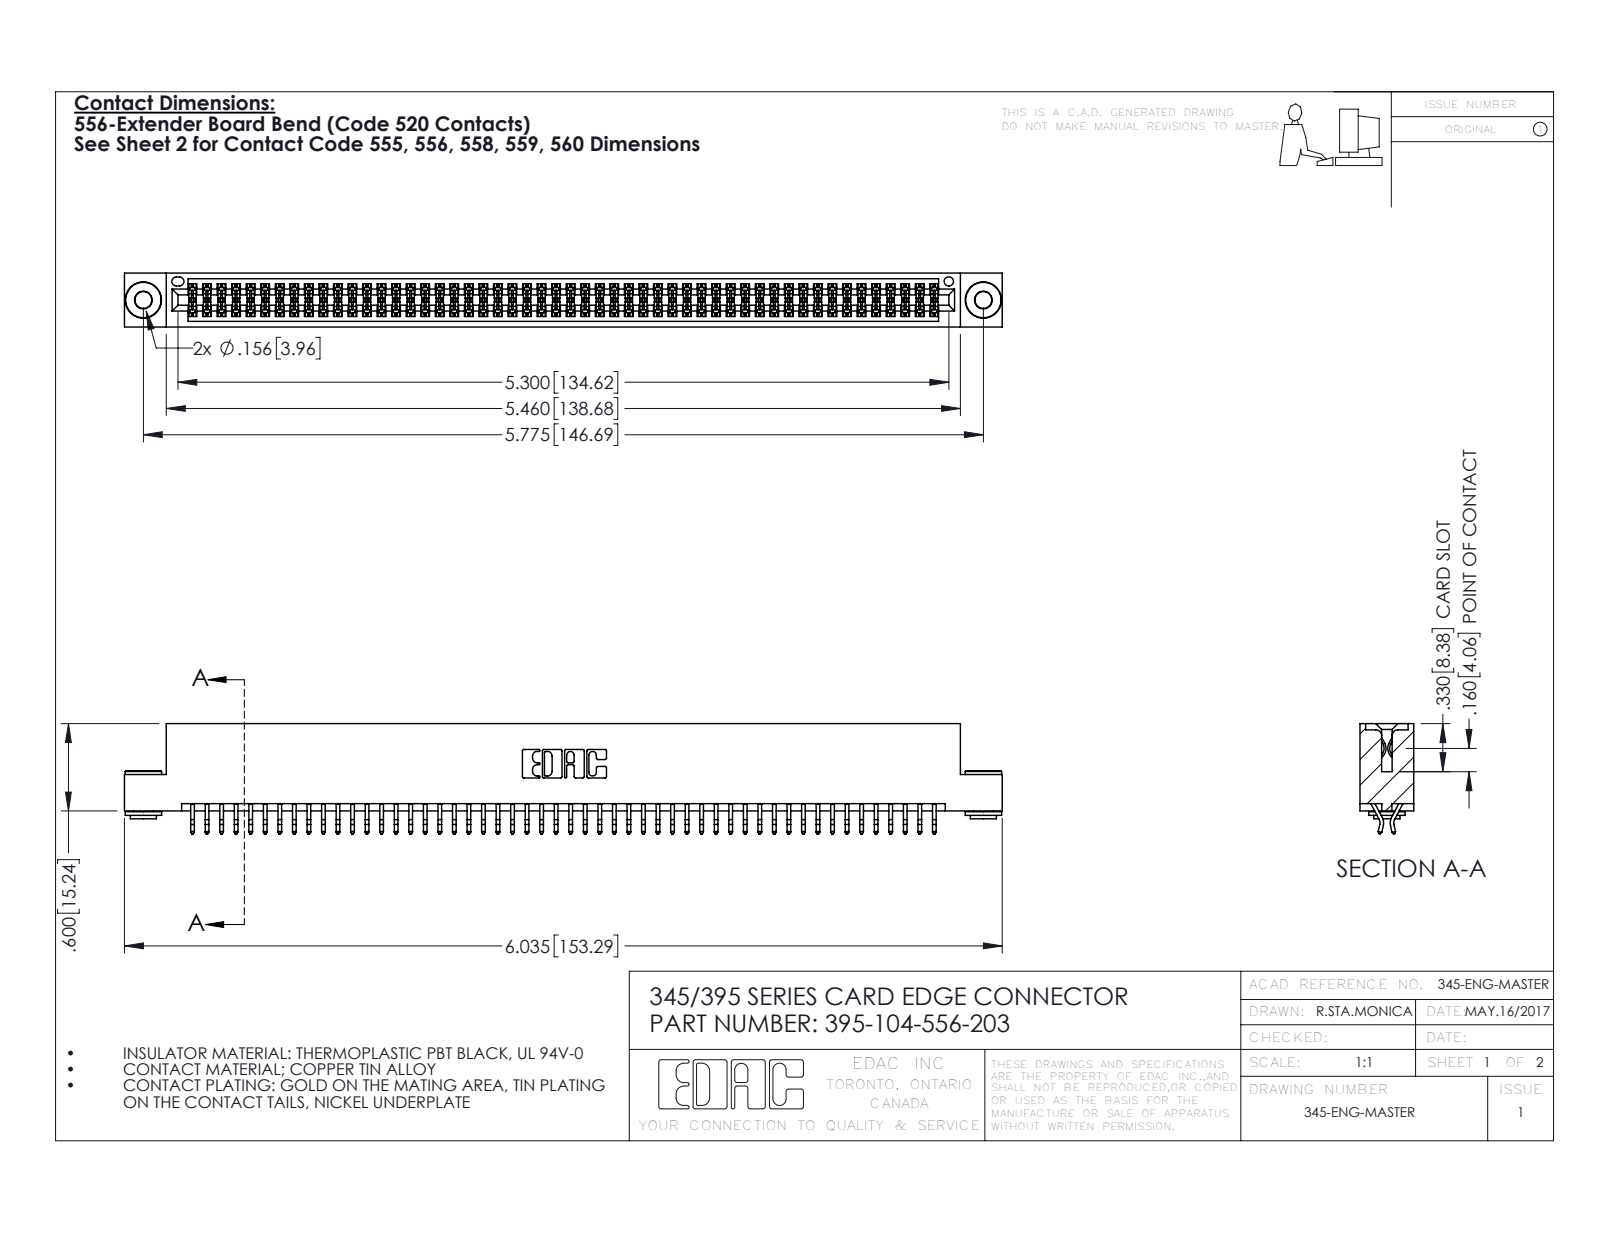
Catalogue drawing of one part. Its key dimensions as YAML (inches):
part_name: "345-250-002_345-250-002-102; 345-292-001_556 Tail; 395-104-556-203; 345 Part_Flush Mounting Lugs - 0.156 Dia-TH"
step_written_by: "SolidWorks 2016 (CONFIG_CONTROL_DESIGN)"
units: inches
bodies: {solids: 107, faces: 5988, planar: 3938, cylindrical: 2042, other: 8}
overall_size: [6.035, 0.757, 0.37]
volume: 0.915
surface_area: 34.84
round_holes:
  - {diameter: 0.116, count: 2}
  - {diameter: 0.156, count: 2}
  - {diameter: 0.064, count: 1}
round_bosses_or_shafts:
  - {diameter: 0.25, count: 2}
  - {diameter: 0.18, count: 2}
  - {diameter: 0.136, count: 2}
partial_cylinders:
  - {radius: 0.006, count: 156}
  - {radius: 0.01, count: 22}
  - {radius: 0.007, count: 6}
  - {radius: 0.031, count: 6}
  - {radius: 0.026, count: 3}
  - {radius: 0.01, count: 2}
  - {radius: 0.014, count: 2}
  - {radius: 0.019, count: 2}
face_to_face_distances: [0.072, 0.298, 0.37, 0.2, 0.025, 0.098, 0.272, 0.225, 0.175, 0.149]
hole_center_spacings: [0.27, 5.539, 5.775]
